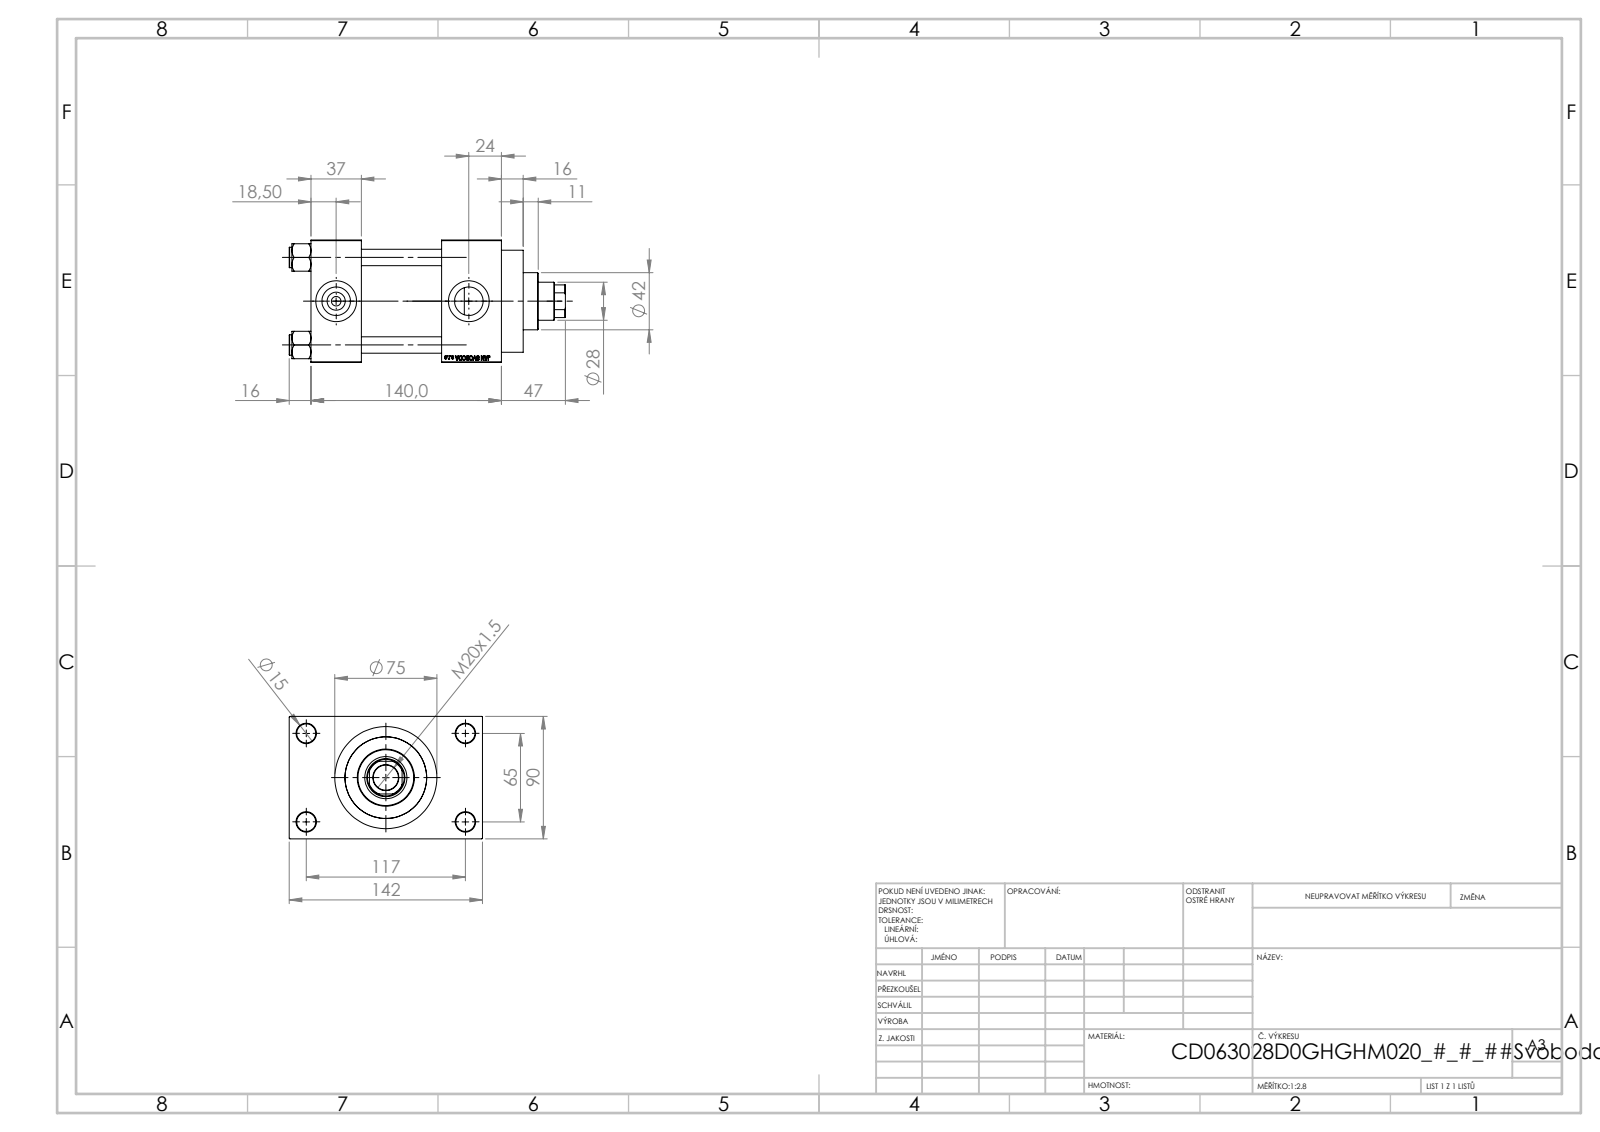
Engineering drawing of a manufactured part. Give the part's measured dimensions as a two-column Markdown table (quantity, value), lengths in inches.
| quantity | value |
| --- | --- |
| part name | V215CD_VCP_D; V215CD_VC_A; V215CD_D_Body; V215CD_D_TYCINKA (+1 more) |
| STEP written by | SolidWorks 2019 (CONFIG_CONTROL_DESIGN) |
| units | inches |
| bodies | 11 solids, 1103 faces (497 planar, 88 cylindrical, 518 other) |
| overall size | 7.992 × 5.591 × 3.543 |
| volume | 66.88 in³ |
| surface area | 310.5 in² |
| round holes (diameter × count) | 0.472 × 4, 0.551 × 4, 0.276 × 2, 0.825 × 2, 1.181 × 2, 0.728 × 1, 1.102 × 1, 1.22 × 1, 1.969 × 1, 2.362 × 1, 2.48 × 1 |
| round bosses / shafts (diameter × count) | 0.591 × 4, 2.953 × 1, 2.717 × 1, 1.654 × 1 |
| partial cylindrical surfaces (radius × count) | 0.531 × 1 |
| main face-to-face distances | 3.543, 2.323, 1.457, 3.78, 5.512, 4.055, 1.732, 1.024, 4.567, 0.63 |
| hole center spacings | 1.037, 1.79, 2.531, 2.635, 2.748, 3.569, 4.383, 2.559 |
